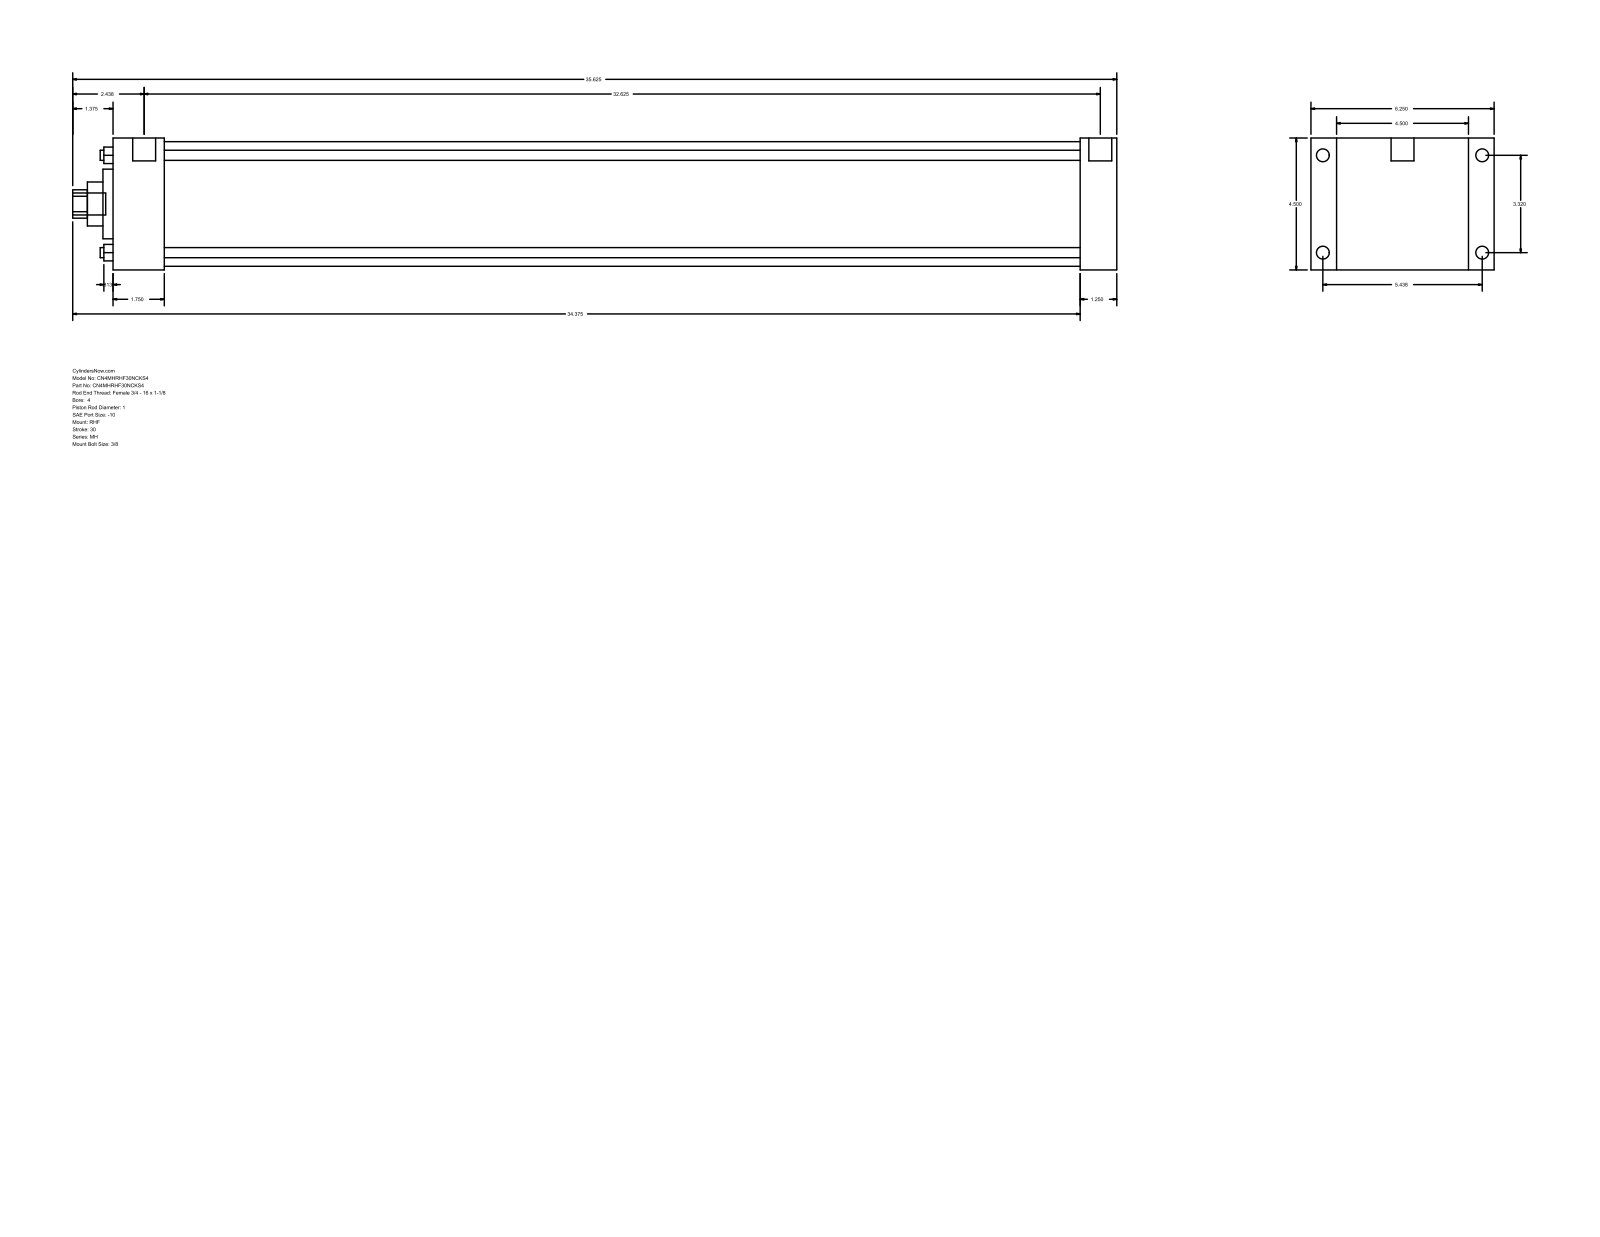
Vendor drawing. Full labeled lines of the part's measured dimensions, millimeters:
Part name (STEP PRODUCT): MH_RHF__0400_1
STEP written by: GSSL Pune (CONFIG_CONTROL_DESIGN)
Units: millimetres
Bodies: 0 solids, 90 faces (61 planar, 29 cylindrical, 0 other)
Overall size (bounding box): 904.88 × 158.75 × 114.3
Round holes (diameter × count): ⌀8.76 ×4, ⌀25.4 ×1, ⌀38.1 ×1, ⌀60.33 ×1, ⌀107.95 ×1
Round bosses / shafts (diameter × count): ⌀11.13 ×4, ⌀8.73 ×4, ⌀19.84 ×2, ⌀19.05 ×1
Partial cylindrical surfaces — rounded edges, fillets, slot ends (radius × count): R12.29 ×1
Main face-to-face distances: 114.3, 869.96, 838.2, 31.76, 22.23, 136.53, 44.46, 793.74, 825.5, 158.76
Hole centre spacings: 59.62, 84.32, 119.25
